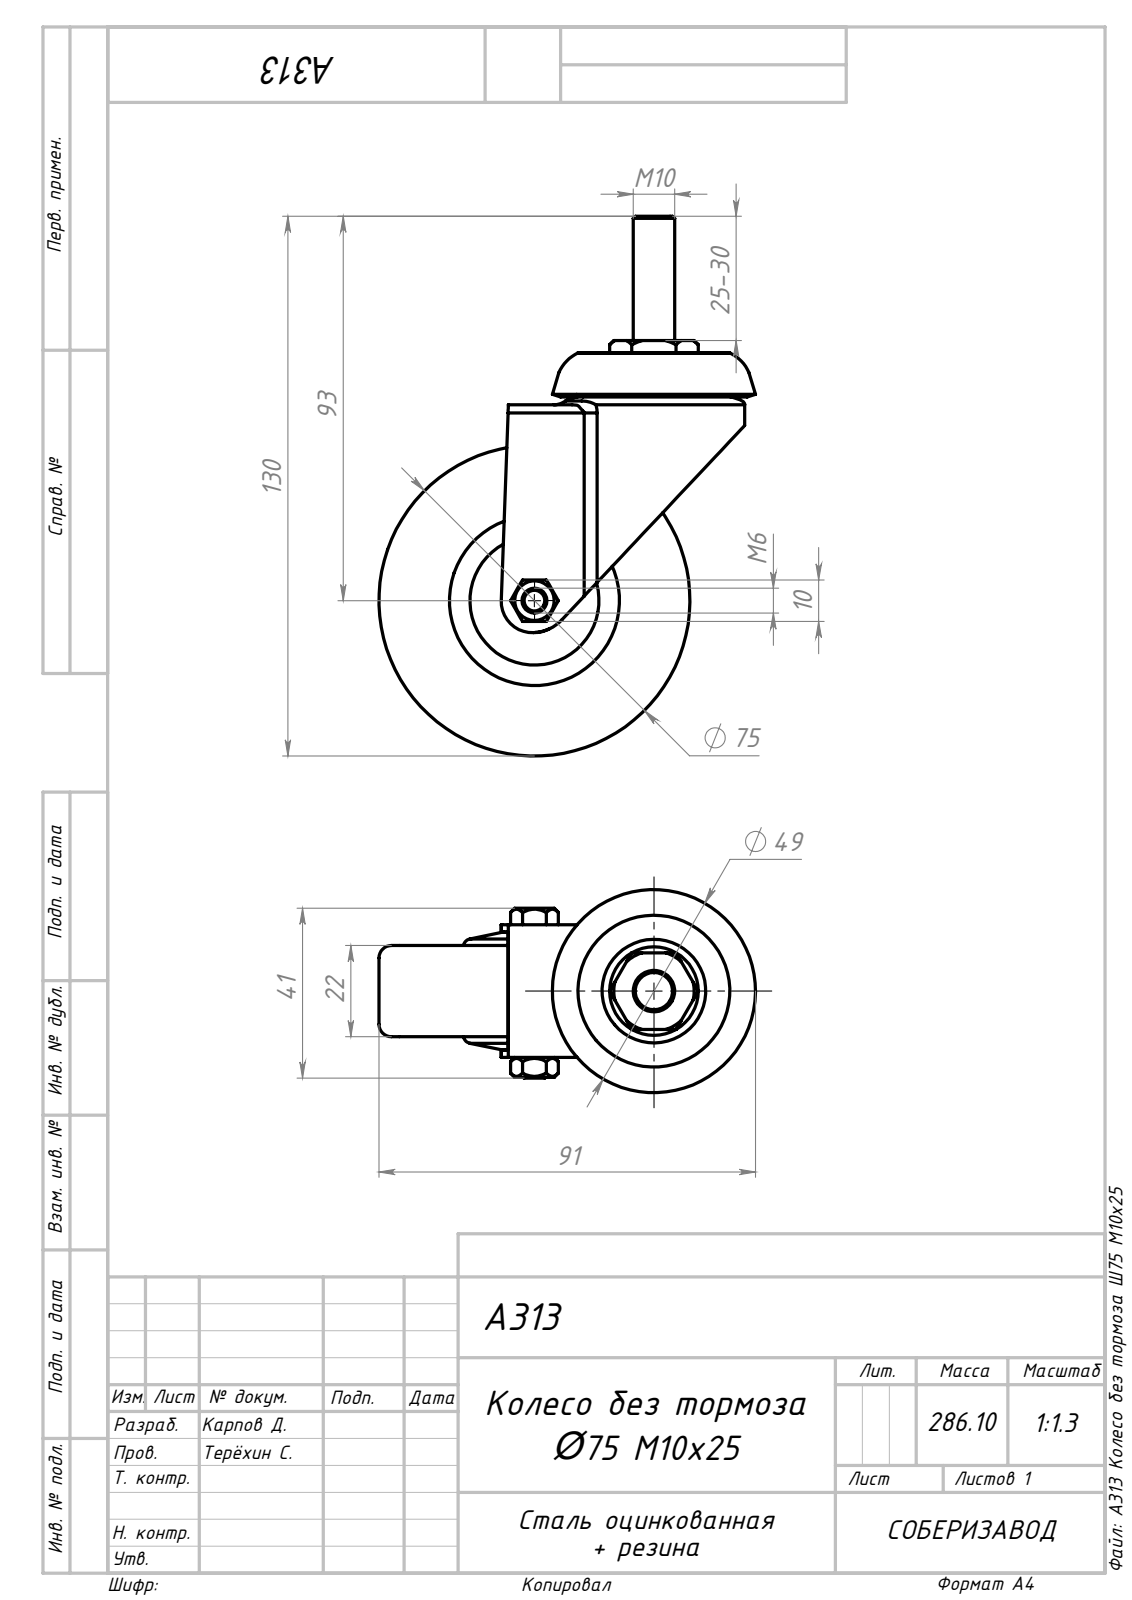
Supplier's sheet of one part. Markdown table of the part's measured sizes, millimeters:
| quantity | value |
| --- | --- |
| part name | Защита_00; A313 Колесо без тормоза O75 М10х25; Дно_00; Крышка_00 (+5 more) |
| STEP written by | SolidWorks 2021 (AUTOMOTIVE_DESIGN) |
| units | millimeters |
| bodies | 9 solids, 234 faces (75 planar, 56 cylindrical, 103 other) |
| overall size | 130.27 × 90.81 × 49 |
| volume | 104 672 mm³ |
| surface area | 45 333 mm² |
| round holes (diameter × count) | 5 × 1, 6 × 1, 8 × 1, 12 × 1, 30.3 × 1, 39 × 1 |
| round bosses / shafts (diameter × count) | 75 × 1, 34.3 × 1, 16 × 1, 10 × 1 |
| partial cylindrical surfaces (radius × count) | 2 × 4, 5 × 2, 7.5 × 1, 10 × 1, 20.15 × 1, 21.9 × 1 |
| main face-to-face distances | 1.75, 25.25, 5, 22, 3.25, 9, 18, 12.25, 16.25, 13 |
